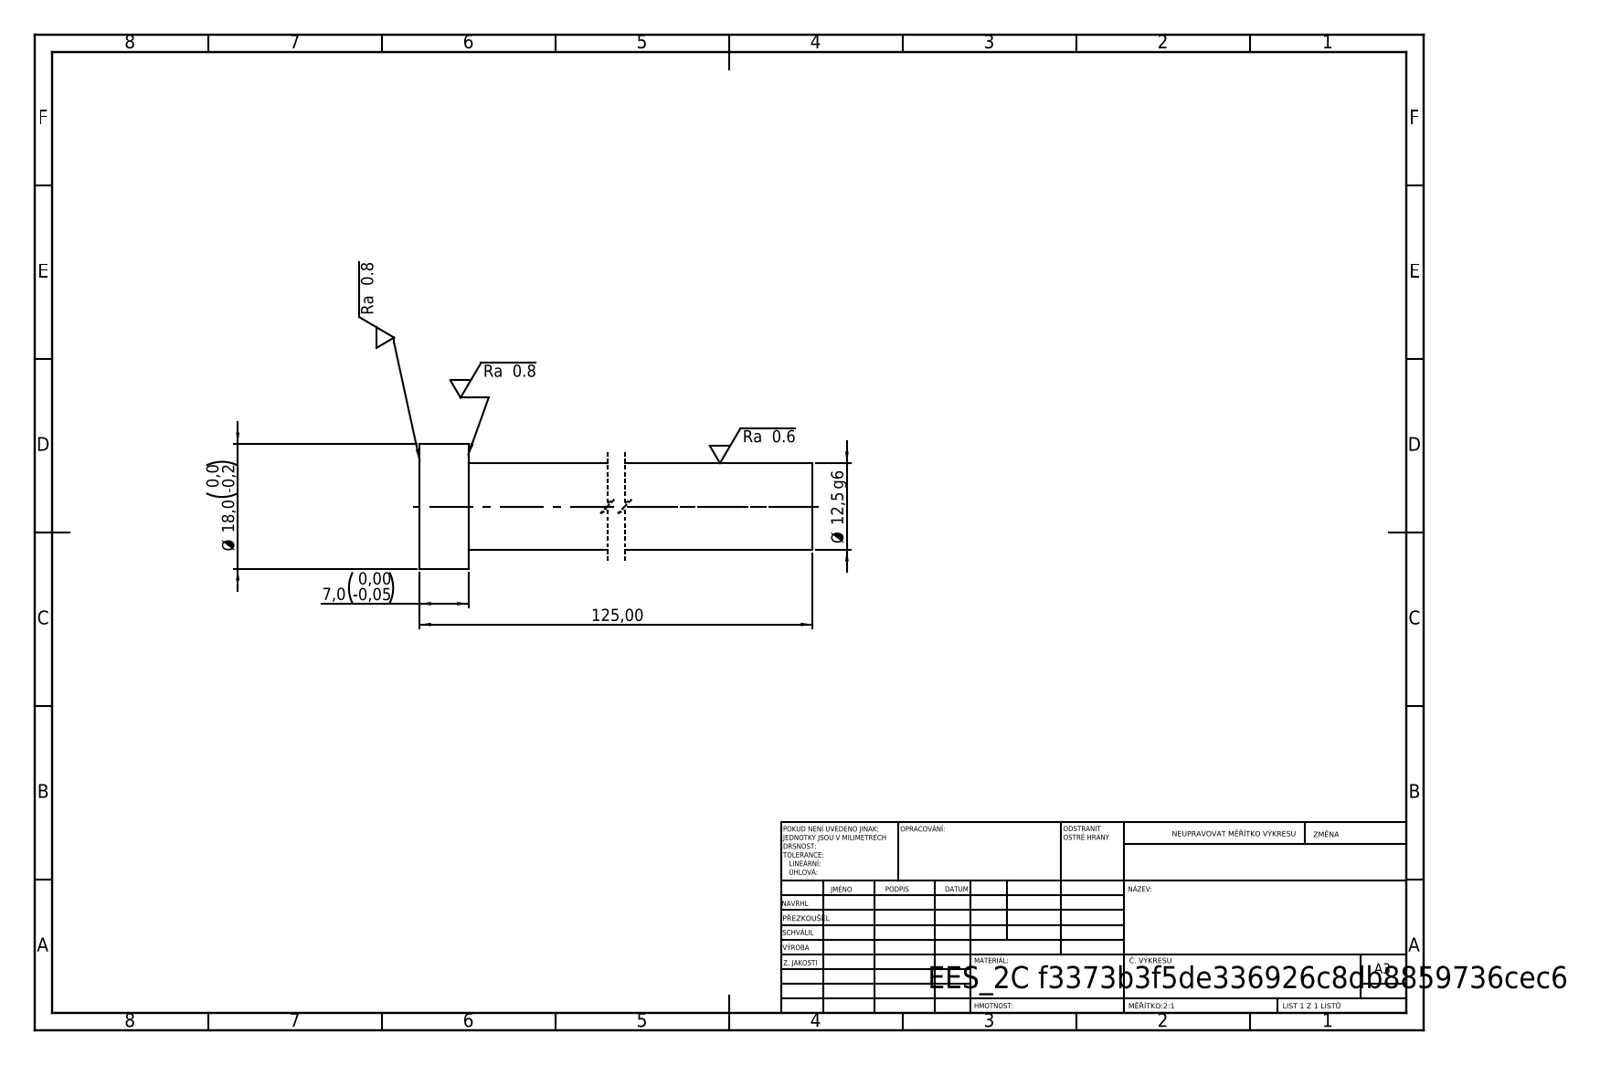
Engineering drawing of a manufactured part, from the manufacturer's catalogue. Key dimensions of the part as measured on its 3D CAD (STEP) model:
STEP written by: SolidWorks 2019 (CONFIG_CONTROL_DESIGN)
Units: millimetres
Bodies: 1 solid, 7 faces (3 planar, 4 cylindrical, 0 other)
Overall size (bounding box): 125 × 18 × 18
Volume: 16 262 mm³ · Surface area: 5 539 mm²
Round bosses / shafts (diameter × count): ⌀18 ×1, ⌀12.5 ×1
Main face-to-face distances: 7, 125, 118
